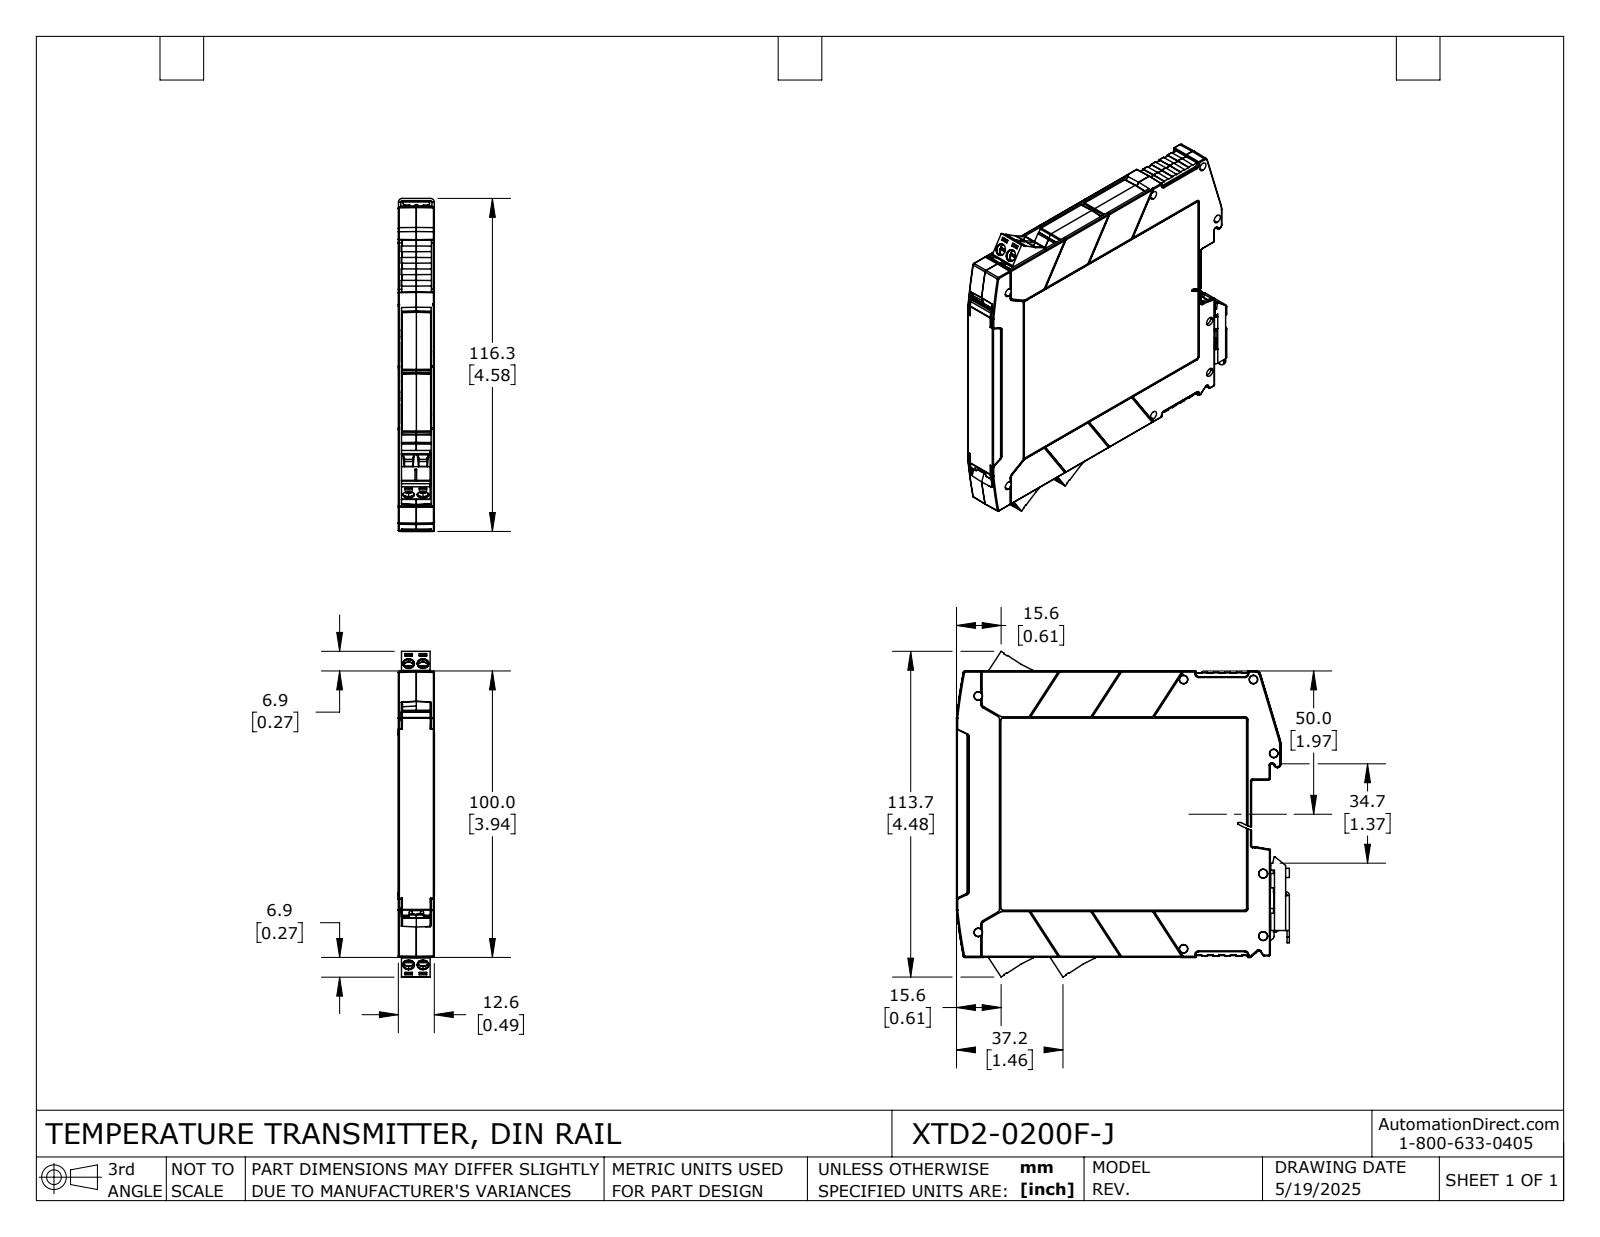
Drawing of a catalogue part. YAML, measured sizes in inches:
part_name: "XTD2-0200F-J"
step_written_by: "SolidWorks 2024 (AUTOMOTIVE_DESIGN)"
units: inches
bodies: {solids: 14, faces: 3337, planar: 1910, cylindrical: 596, other: 831}
overall_size: [4.577, 4.478, 0.496]
volume: 2.41
surface_area: 101.5
round_holes:
  - {diameter: 0.063, count: 6}
  - {diameter: 0.11, count: 6}
  - {diameter: 0.152, count: 6}
  - {diameter: 0.159, count: 6}
round_bosses_or_shafts:
  - {diameter: 0.156, count: 6}
  - {diameter: 0.098, count: 6}
  - {diameter: 0.059, count: 2}
  - {diameter: 0.053, count: 2}
partial_cylinders:
  - {radius: 0.008, count: 89}
  - {radius: 0.012, count: 78}
  - {radius: 0.02, count: 71}
  - {radius: 0.039, count: 22}
  - {radius: 0.004, count: 20}
  - {radius: 0.016, count: 13}
  - {radius: 0.006, count: 12}
  - {radius: 0.028, count: 8}
face_to_face_distances: [0.049, 0.445, 0.494, 0.396, 0.043, 0.451, 0.402, 0.031, 0.198, 0.247]
hole_center_spacings: [0.197, 0.464, 0.504, 0.713, 0.739]
